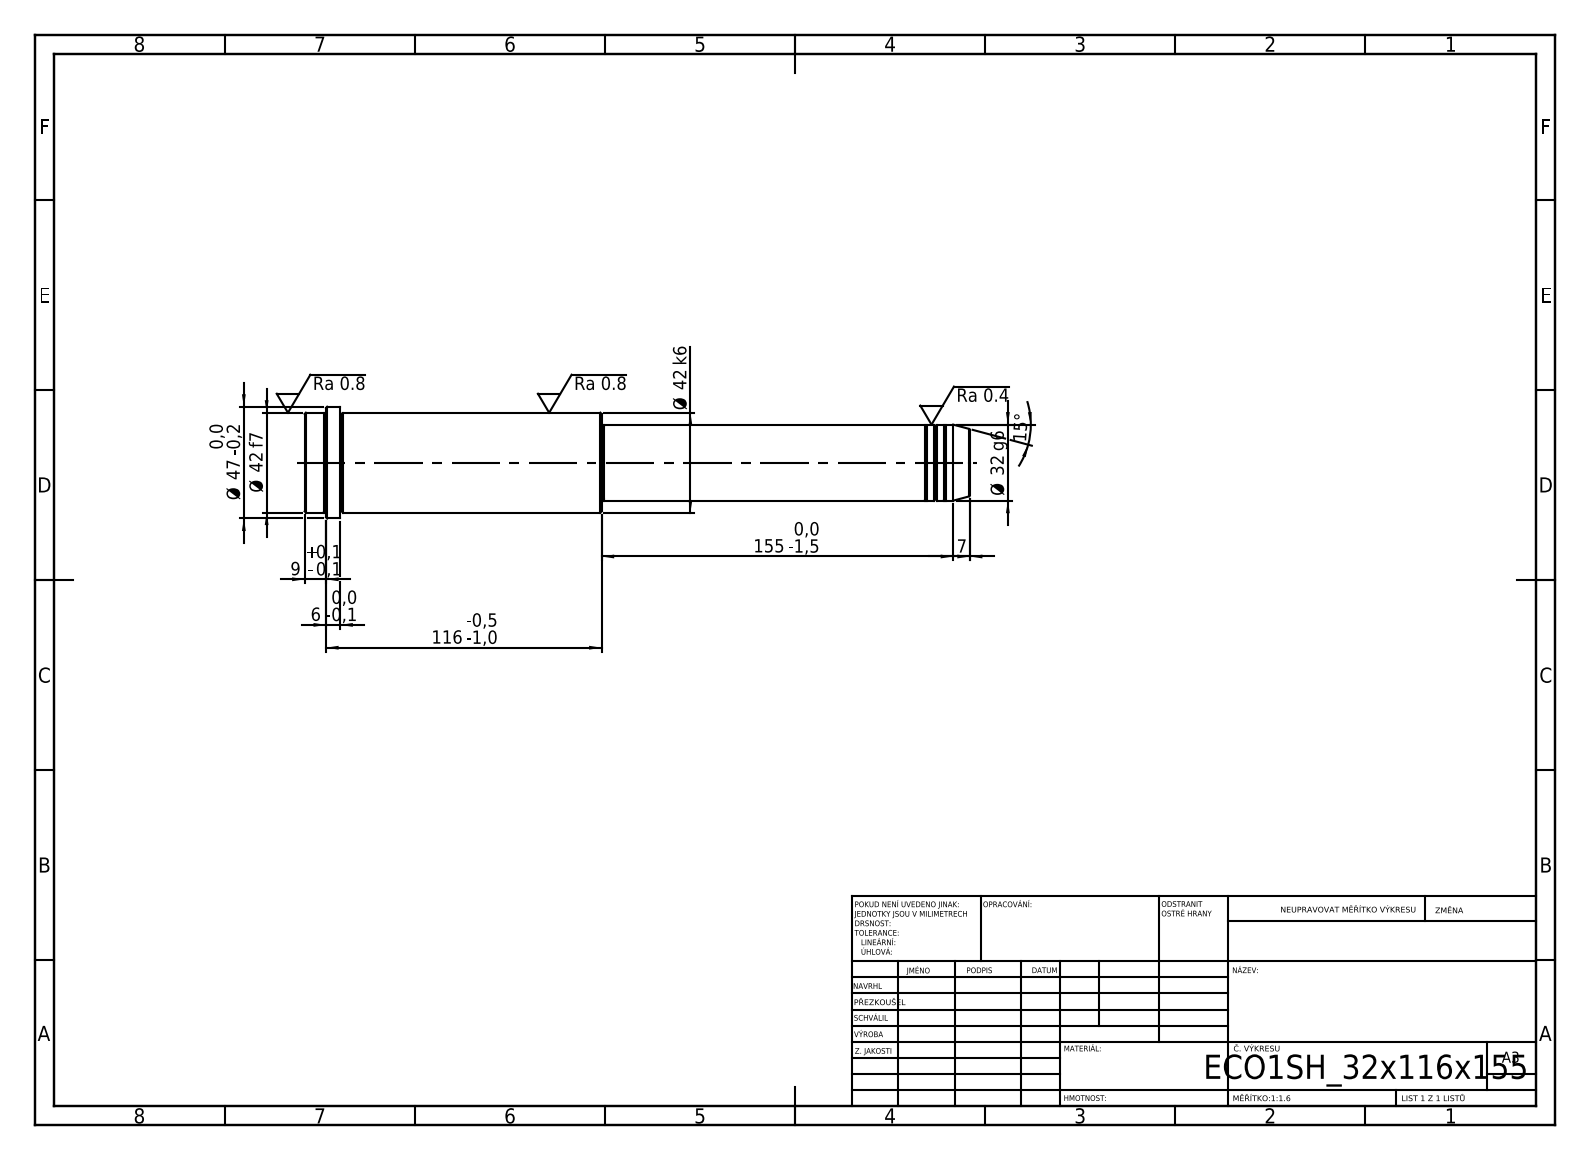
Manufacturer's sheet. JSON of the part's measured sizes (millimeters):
{"step_written_by": "SolidWorks 2019 (CONFIG_CONTROL_DESIGN)", "units": "millimeters", "bodies": {"solids": 1, "faces": 52, "planar": 6, "cylindrical": 16, "other": 30}, "overall_size": [280, 47, 47], "volume_mm3": 298979, "surface_area_mm2": 35716, "round_bosses_or_shafts": [[47, 1], [42, 1], [32, 1], [31, 1]], "face_to_face_distances": [280, 155, 125, 265, 110, 15, 271, 116, 6, 9]}
